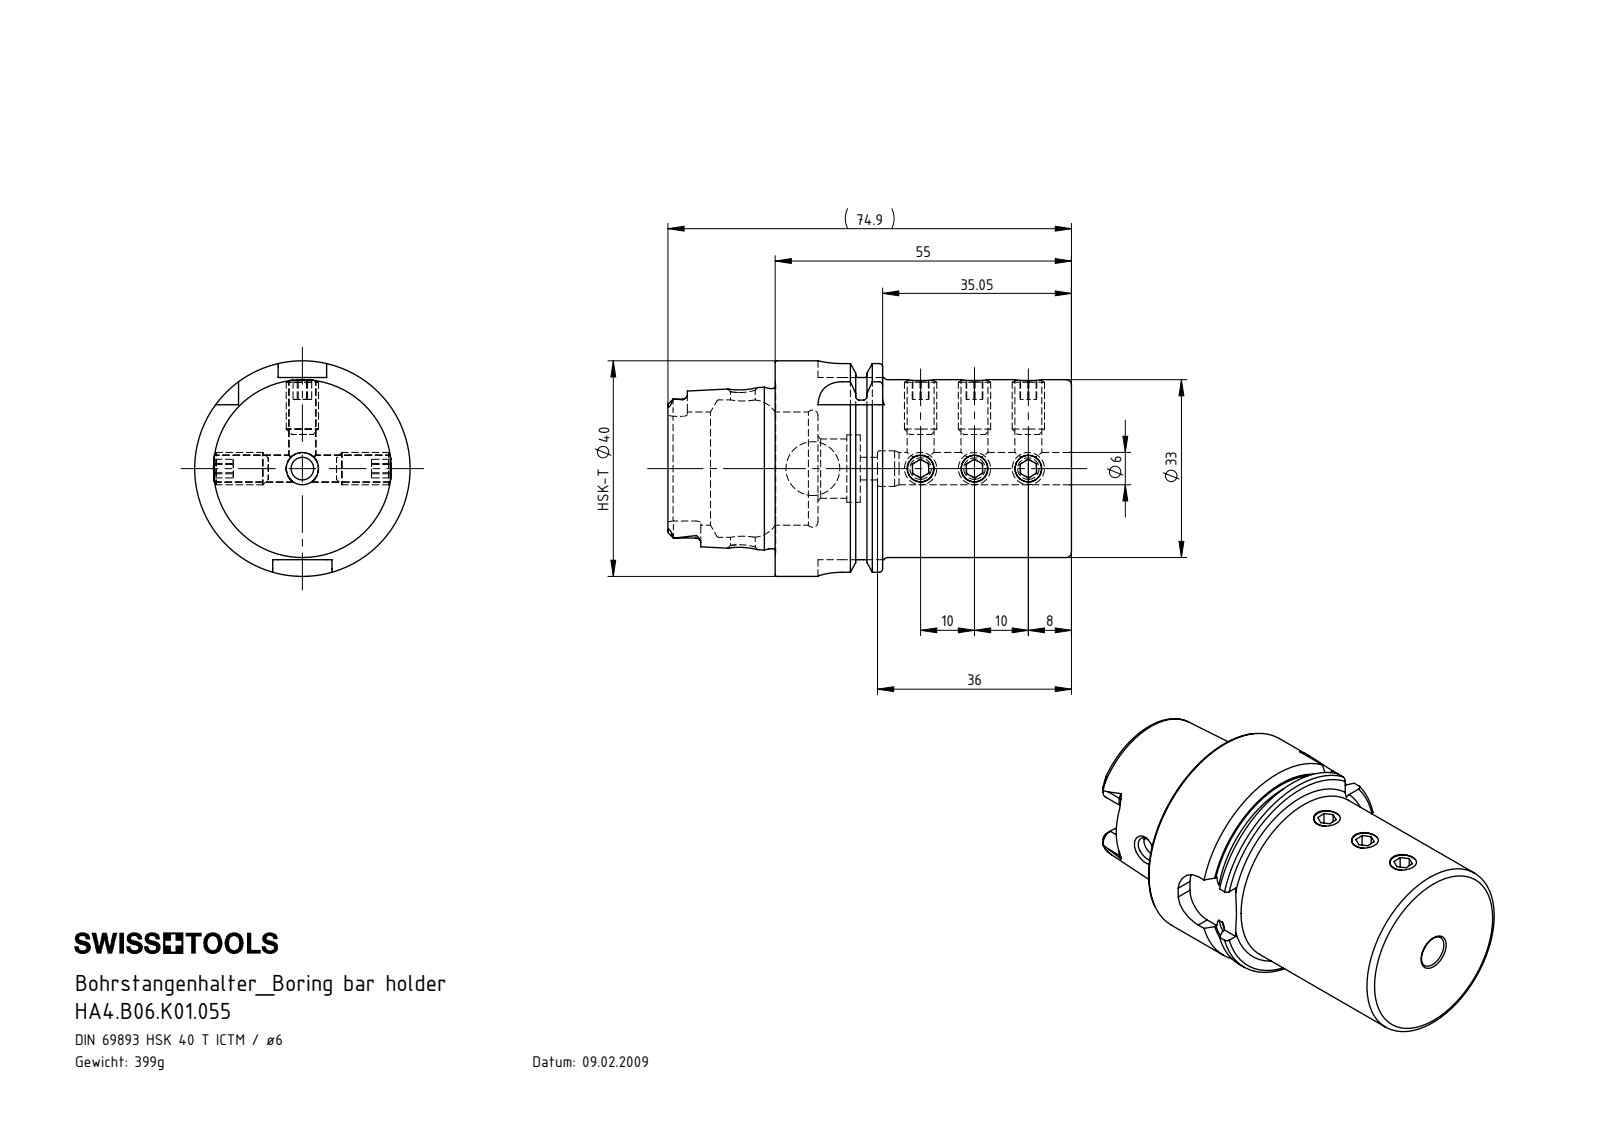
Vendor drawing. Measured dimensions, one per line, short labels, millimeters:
name: HA4-B06.K01.055_C_Fertigbearbeitung; HA4.B06.K01.055; ISO 4026 - M6 x 10_PreviewCfg
written by: SolidWorks 2017 (AUTOMOTIVE_DESIGN)
unit: mm
bodies: 10 solids, 322 faces (128 planar, 89 cylindrical, 105 other)
size: 74.9 × 40 × 40
volume: 52 816 mm³; area: 17 757 mm²
holes: 6× ⌀5, 1× ⌀4.2, 1× ⌀4.6, 1× ⌀6, 1× ⌀6.6, 1× ⌀10, 1× ⌀11, 1× ⌀12.5, 1× ⌀21, 1× ⌀25.5
bosses: 6× ⌀6, 1× ⌀40, 1× ⌀34.75, 1× ⌀33, 1× ⌀29.71
rounds: 6× R0.9, 4× R1.88, 4× R4.5
face distances: 55, 7.95, 47.05, 19.95, 12, 35.05, 19.9, 27.85, 39.85, 74.9
hole spacings: 10, 20, 30, 33, 40, 43, 53
